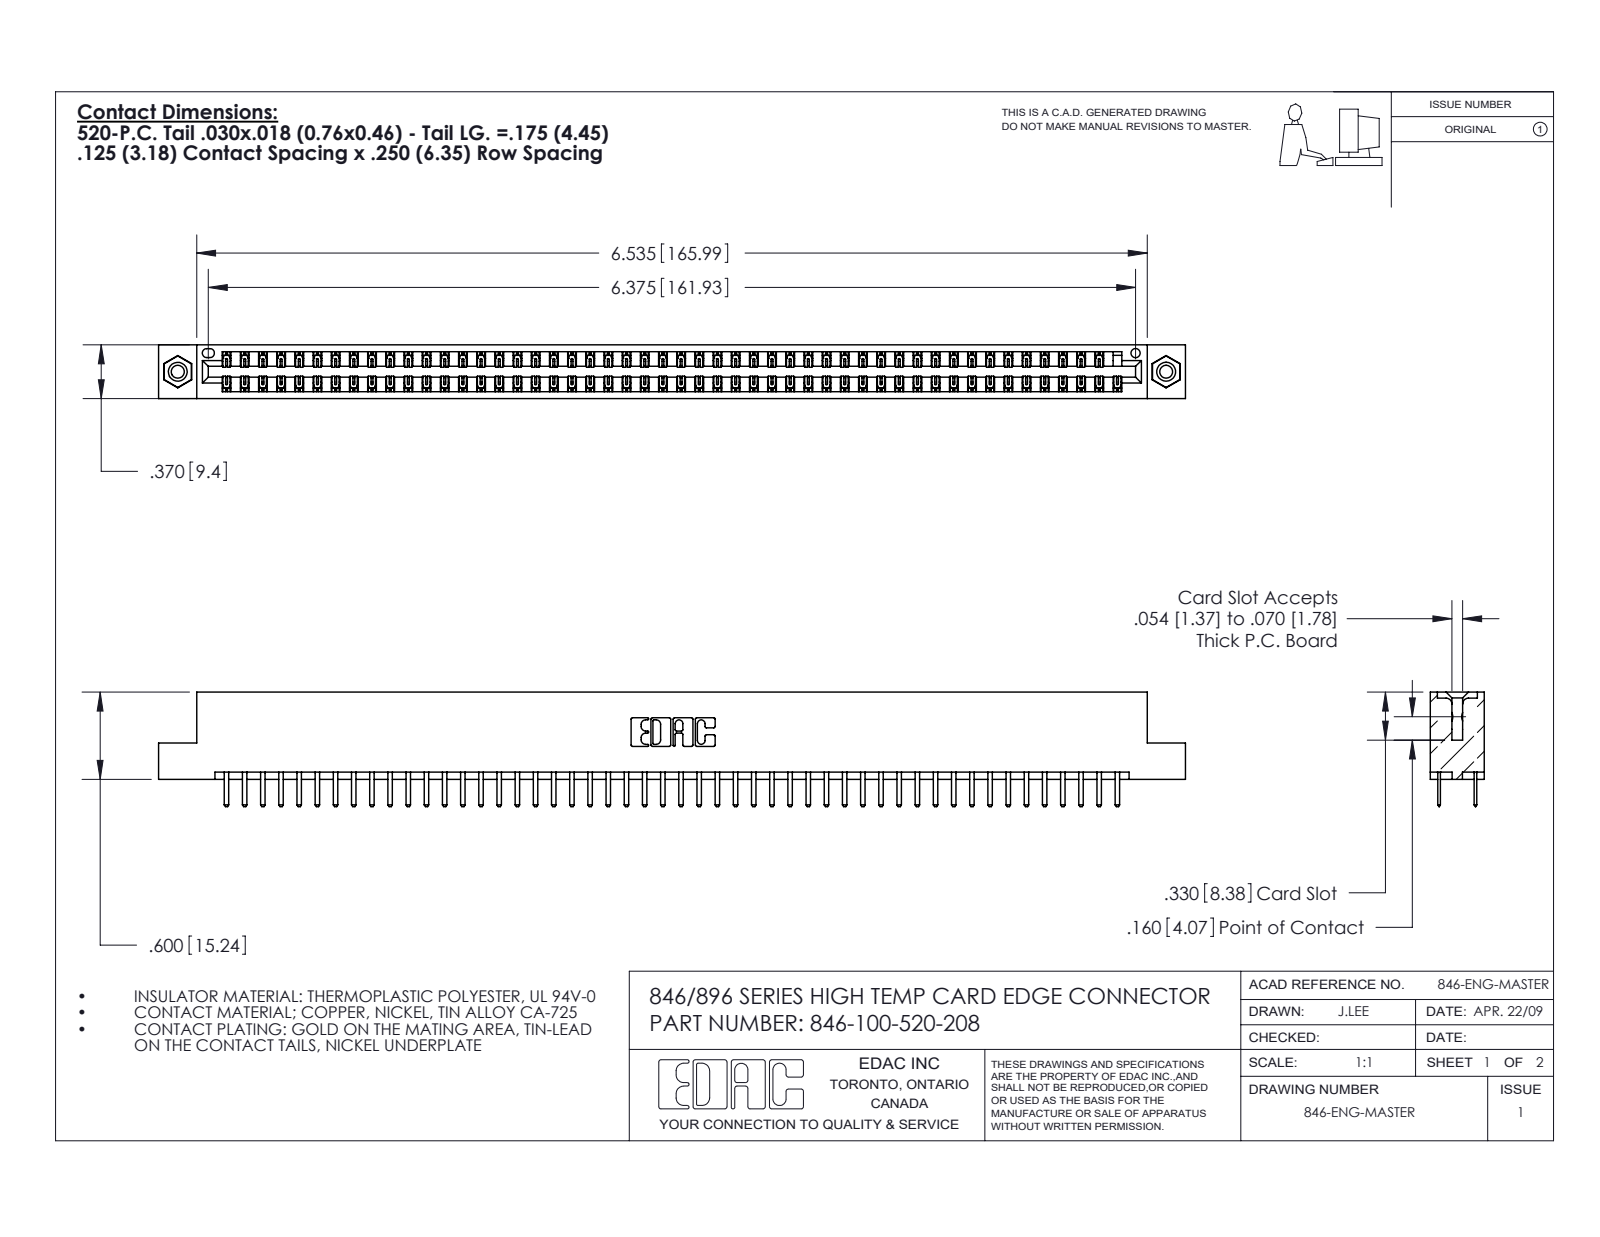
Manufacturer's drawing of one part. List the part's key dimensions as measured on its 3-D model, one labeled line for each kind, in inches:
Part name (STEP PRODUCT): 346-100-520-208; 345-292-001_345-293-120; 345-250-001_345-250-003-102; 346 Part_Flush Mounting Lugs - 0.156 Dia-TI
STEP written by: SolidWorks 2016 (CONFIG_CONTROL_DESIGN)
Units: inches
Bodies: 103 solids, 5782 faces (3808 planar, 1958 cylindrical, 16 other)
Overall size (bounding box): 7.06 × 0.788 × 0.37
Volume: 1.055 in³ · Surface area: 37.53 in²
Round holes (diameter × count): ⌀0.089 ×2, ⌀0.125 ×2, ⌀0.156 ×2, ⌀0.064 ×1
Round bosses / shafts (diameter × count): ⌀0.155 ×2
Partial cylindrical surfaces — rounded edges, fillets, slot ends (radius × count): R0.006 ×150, R0.01 ×104, R0.01 ×22, R0.007 ×6, R0.031 ×6, R0.026 ×3, R0.014 ×2, R0.022 ×2
Main face-to-face distances: 0.048, 0.322, 0.25, 0.37, 0.275, 0.072, 0.298, 0.025, 0.148, 0.222
Hole centre spacings: 0.246, 6.586, 6.795
